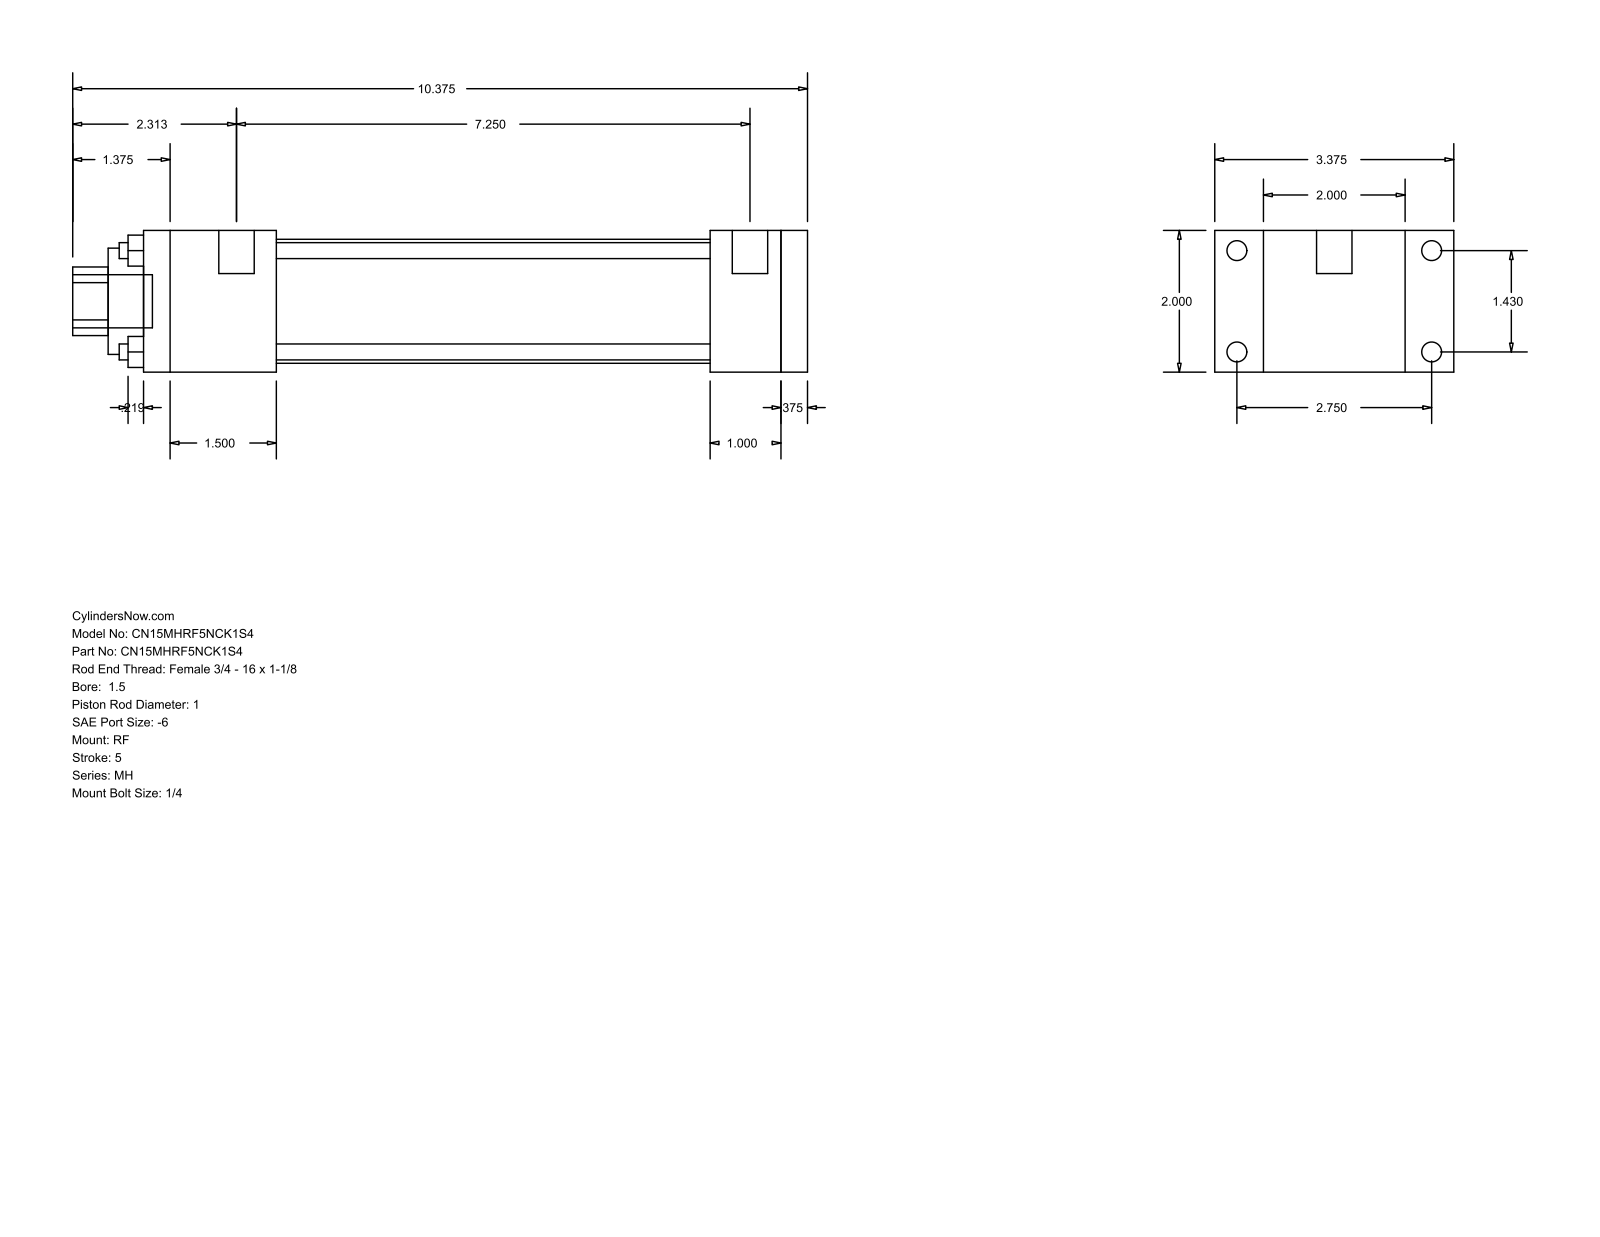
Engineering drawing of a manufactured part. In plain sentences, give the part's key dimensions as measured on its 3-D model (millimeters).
The part is named "MH_RF__0150_1". Its 3-D file was written by "GSSL Pune (CONFIG_CONTROL_DESIGN)". It is 0 solids with 92 faces: 64 planar, 28 cylindrical and 0 other. Overall it measures 263.52 by 85.72 by 50.8 millimeters. Round holes: 4 of diameter 5.71, 1 of diameter 25.4, 1 of diameter 38.1, 1 of diameter 44.45. Round bosses or shafts: 4 of diameter 7.14, 4 of diameter 5.56, 2 of diameter 12.7, 1 of diameter 19.05. Partial cylindrical surfaces (rounded edges, fillets, slot ends): 1 of radius 12.29. The main face-to-face distances are 50.8, 9.52, 228.6, 25.4, 238.12, 17.46, 68.26, 203.2, 34.92, 47.63. The hole center spacings are 25.68, 36.32, 51.36.
